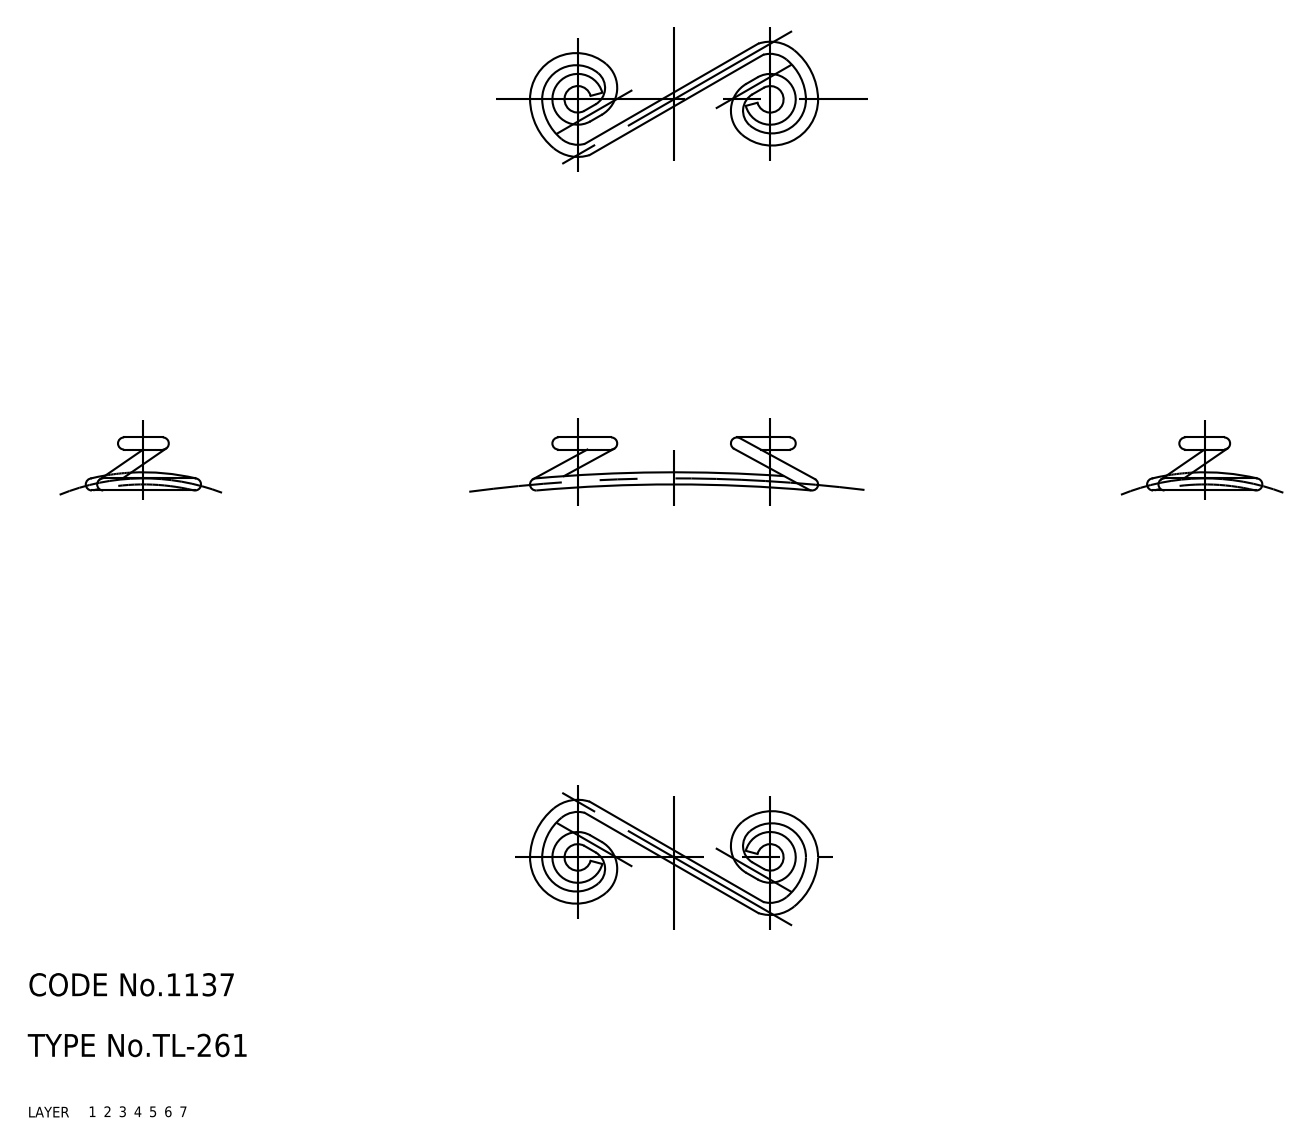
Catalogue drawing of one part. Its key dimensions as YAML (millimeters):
part_name: "spring"
step_written_by: "CADfix (AUTOMOTIVE_DESIGN)"
units: millimeters
bodies: {solids: 1, faces: 28, planar: 0, cylindrical: 0, other: 28}
overall_size: [38.01, 15.07, 7]
volume: 232
surface_area: 585
